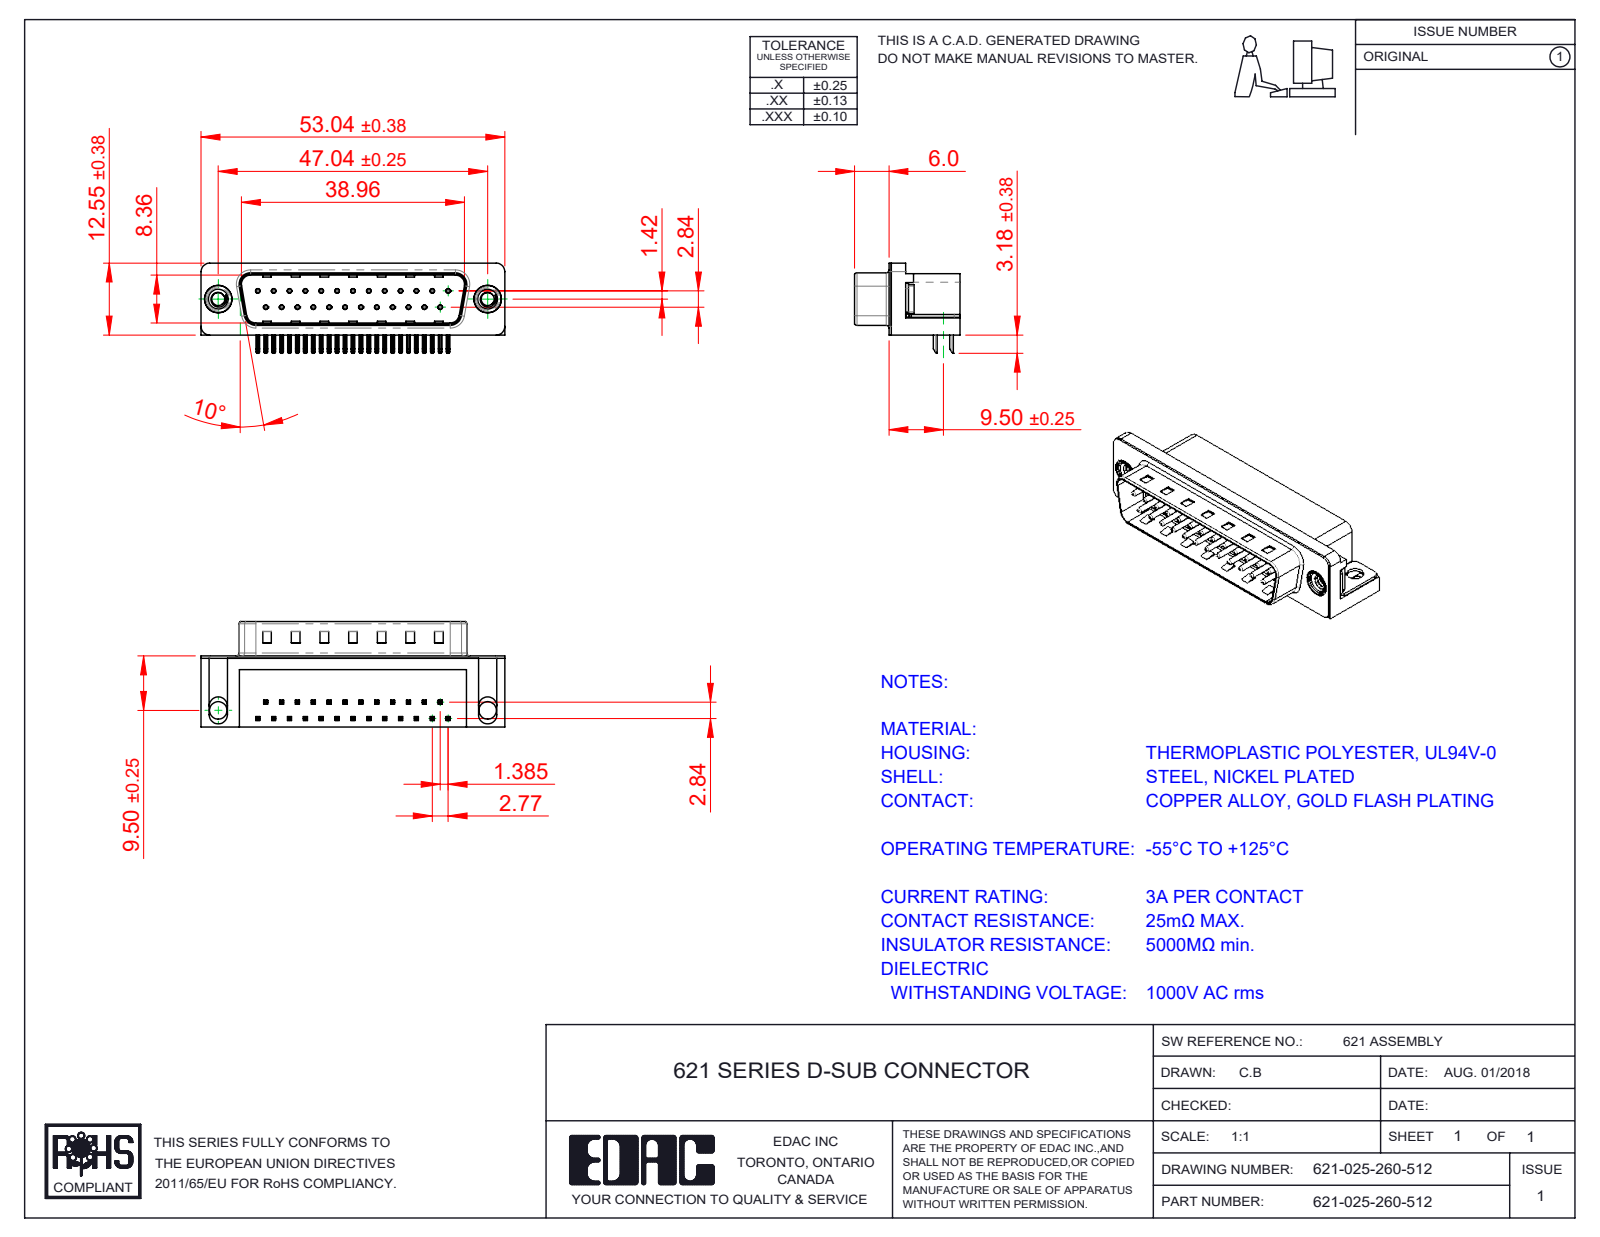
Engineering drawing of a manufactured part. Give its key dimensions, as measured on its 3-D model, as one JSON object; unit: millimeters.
{"part_name": "621 Thru Hole Board Mount; 621 Housing_25 Socket; 621-025-260-512; 621 Shell_25 Socket (+3 more)", "step_written_by": "SolidWorks 2016 (CONFIG_CONTROL_DESIGN)", "units": "millimeters", "bodies": {"solids": 31, "faces": 2261, "planar": 1403, "cylindrical": 659, "other": 199}, "overall_size": [53.04, 18.4, 15.73], "volume_mm3": 6347, "surface_area_mm2": 7670, "round_holes": [[0.35, 25], [0.8, 25], [2.26, 2], [3.05, 2], [4, 2], [4.8, 2], [5, 2]], "round_bosses_or_shafts": [[0.75, 25], [4.9, 2], [4.75, 2], [3.9, 2]], "partial_cylinders_radius": [[0.25, 108], [0.12, 50], [1, 16], [0.5, 9], [1.6, 8], [1.5, 7], [0.9, 4], [2, 4]], "face_to_face_distances": [0.4, 12, 10.35, 2.1, 8.76, 10.46, 1.7, 10.86, 12.4, 9], "hole_center_spacings": [3.16, 2.77, 5.54, 8.31, 11.08, 13.85, 16.62, 5.03]}
